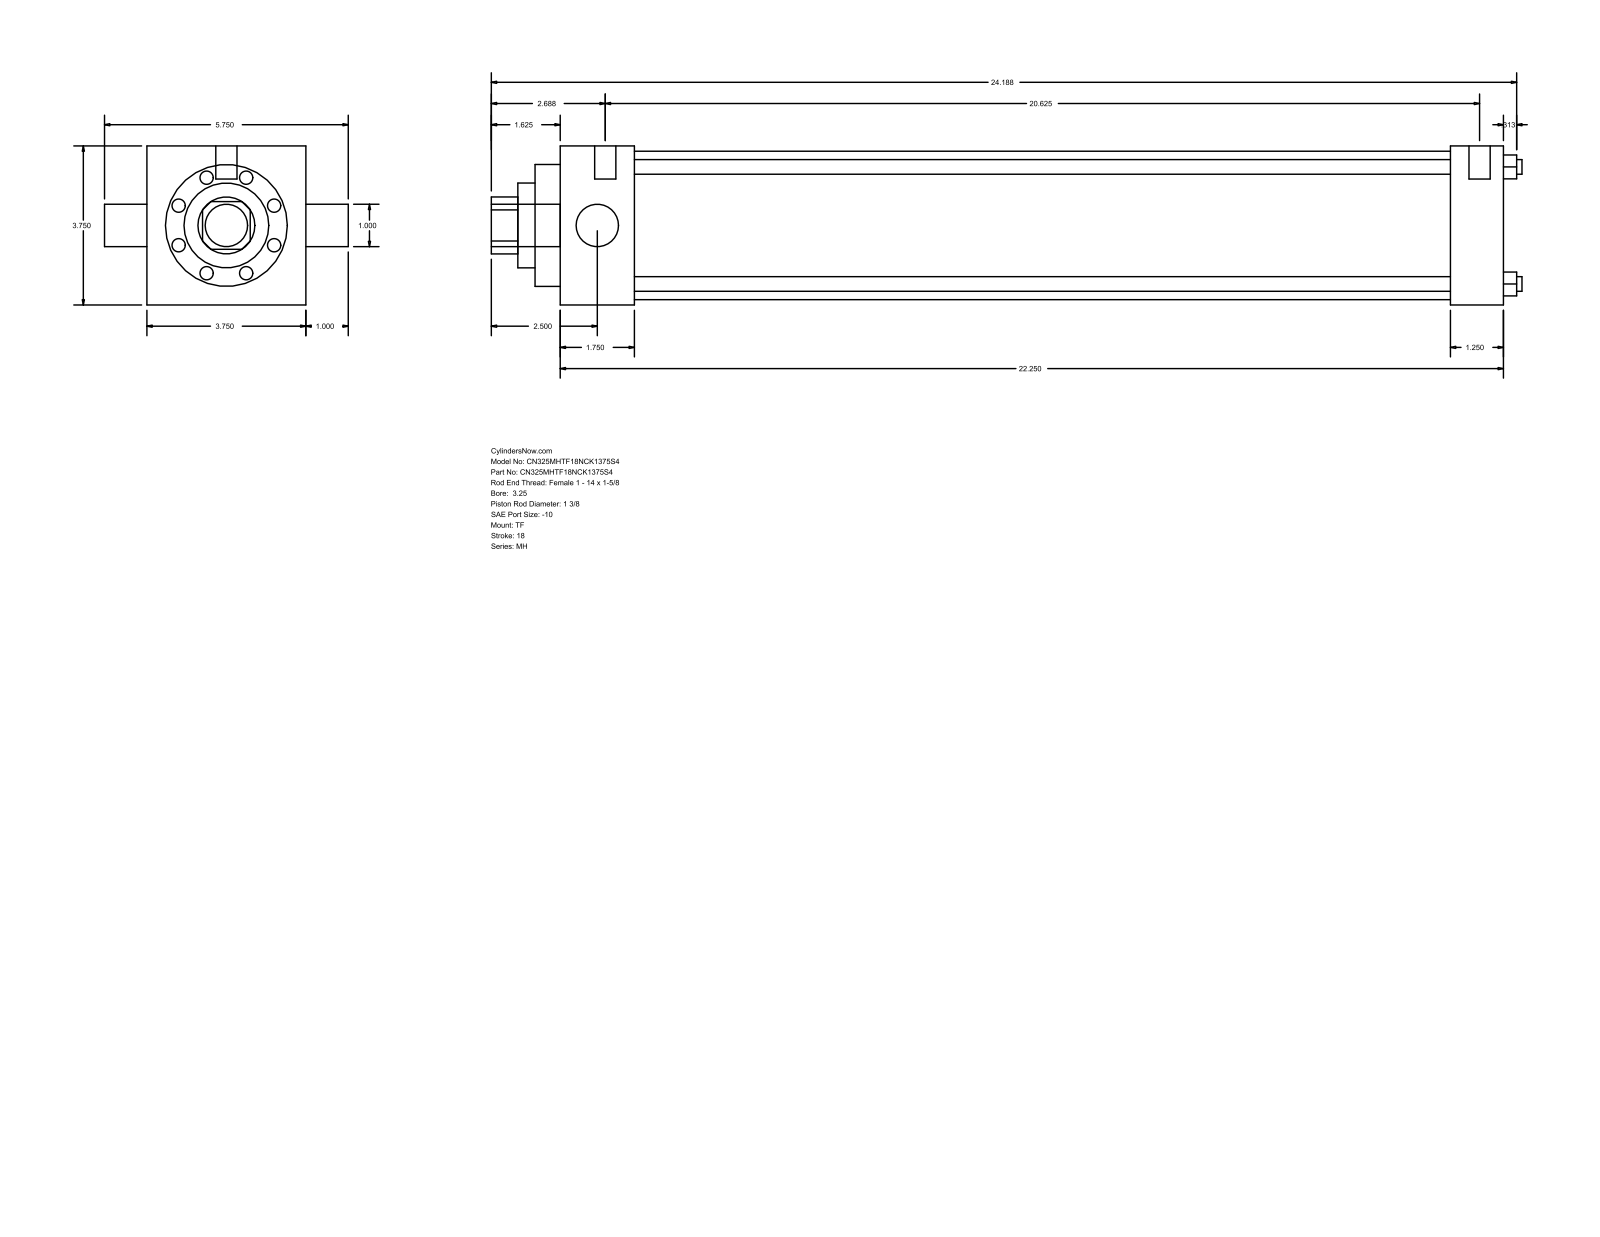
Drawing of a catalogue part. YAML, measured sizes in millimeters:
part_name: "MH_TF__0325_1.375"
step_written_by: "GSSL Pune (CONFIG_CONTROL_DESIGN)"
units: millimeters
bodies: {solids: 0, faces: 86, planar: 61, cylindrical: 25, other: 0}
overall_size: [617.54, 146.05, 95.25]
round_holes:
  - {diameter: 8.76, count: 4}
  - {diameter: 25.4, count: 1}
  - {diameter: 34.92, count: 1}
  - {diameter: 50.8, count: 1}
  - {diameter: 73.03, count: 1}
  - {diameter: 88.9, count: 1}
round_bosses_or_shafts:
  - {diameter: 5.56, count: 3}
  - {diameter: 12.7, count: 2}
  - {diameter: 25.4, count: 1}
partial_cylinders:
  - {radius: 17.06, count: 1}
face_to_face_distances: [95.24, 565.15, 44.45, 533.4, 488.95, 520.7, 31.75, 15.08, 59.53, 548.48]
hole_center_spacings: [49.57, 70.1, 99.14]
